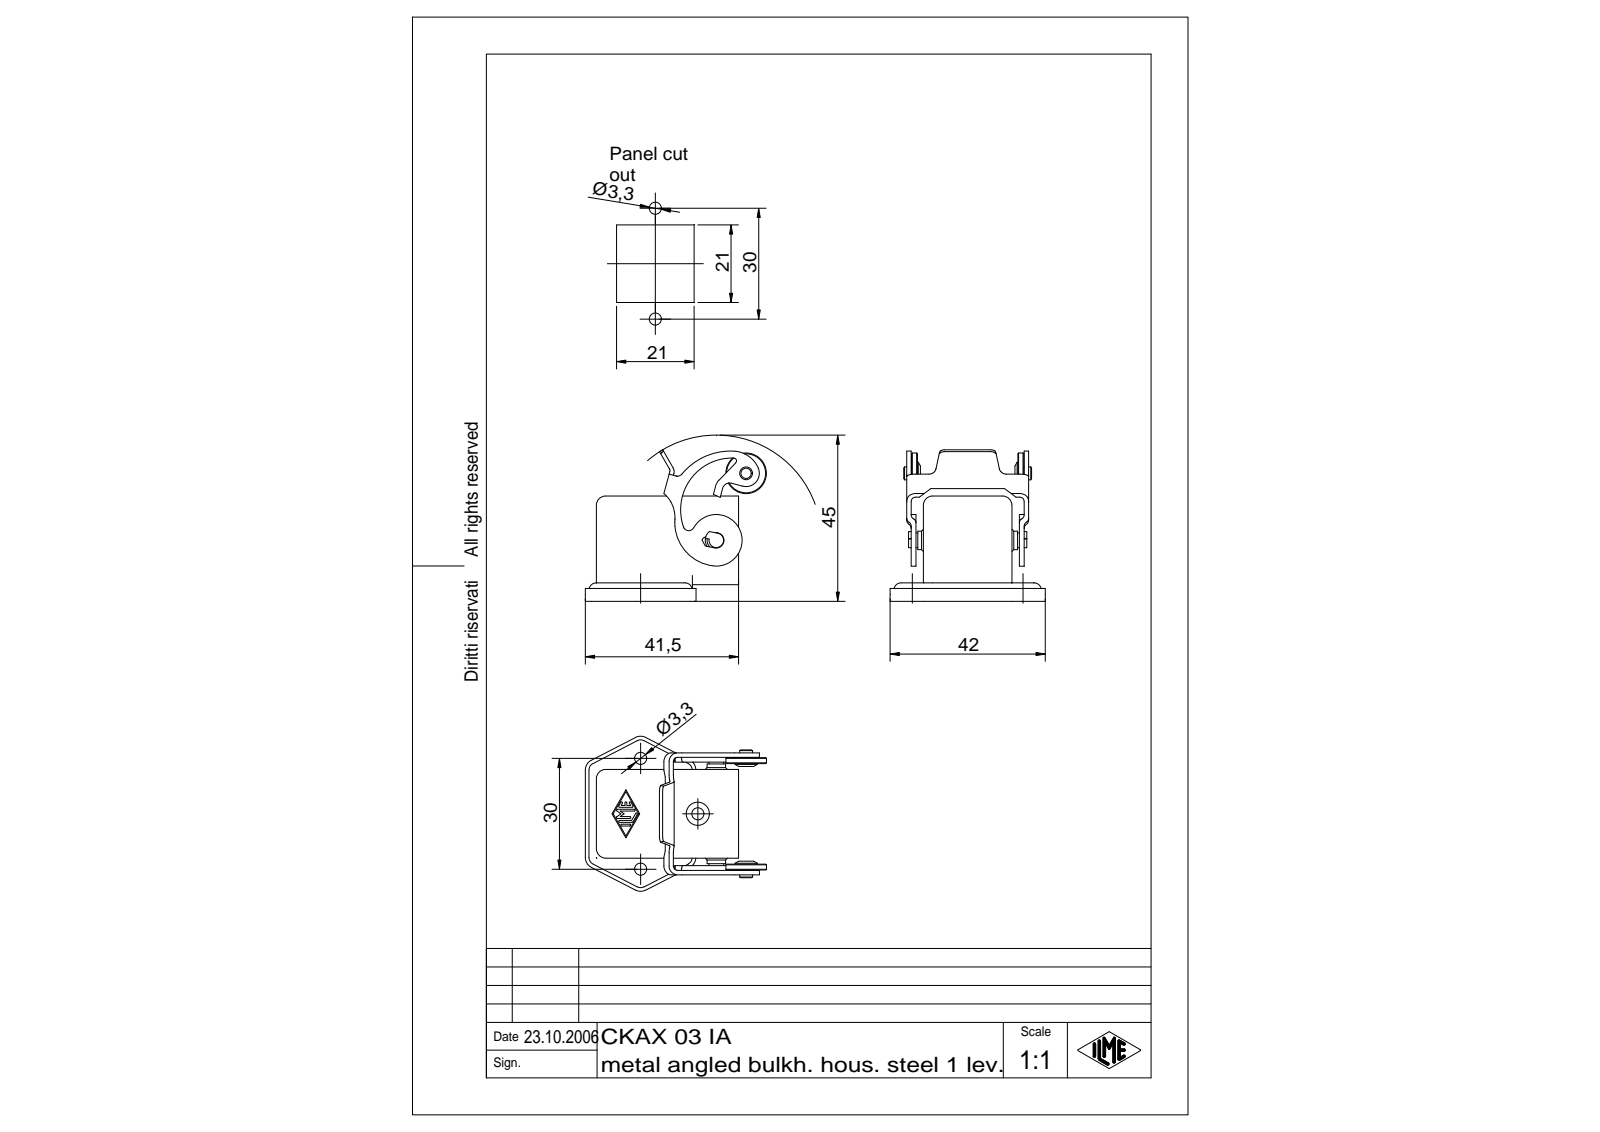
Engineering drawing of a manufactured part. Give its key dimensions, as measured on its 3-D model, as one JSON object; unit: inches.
{"part_name": "CKAX 03 IA", "step_written_by": "Autodesk Inventor 7 (AUTOMOTIVE_DESIGN)", "units": "inches", "bodies": {"solids": 1, "faces": 327, "planar": 121, "cylindrical": 145, "other": 61}, "overall_size": [1.932, 1.654, 1.615], "volume_in3": 0.521, "surface_area_in2": 18.23, "round_holes": [[0.13, 3], [0.134, 2]], "round_bosses_or_shafts": [[0.433, 1], [0.236, 1], [0.197, 1], [0.157, 1], [0.138, 1], [0.126, 1]], "partial_cylinders_radius": [[0.079, 16], [0.01, 14], [0.047, 8], [0.069, 8], [0.098, 7], [0.118, 7], [0.049, 4], [0.059, 2]], "face_to_face_distances": [0.049, 0.896, 0.846, 0.945, 1.122, 1.073, 0.226, 0.079, 0.128, 0.177], "hole_center_spacings": [0.849, 1.181]}
